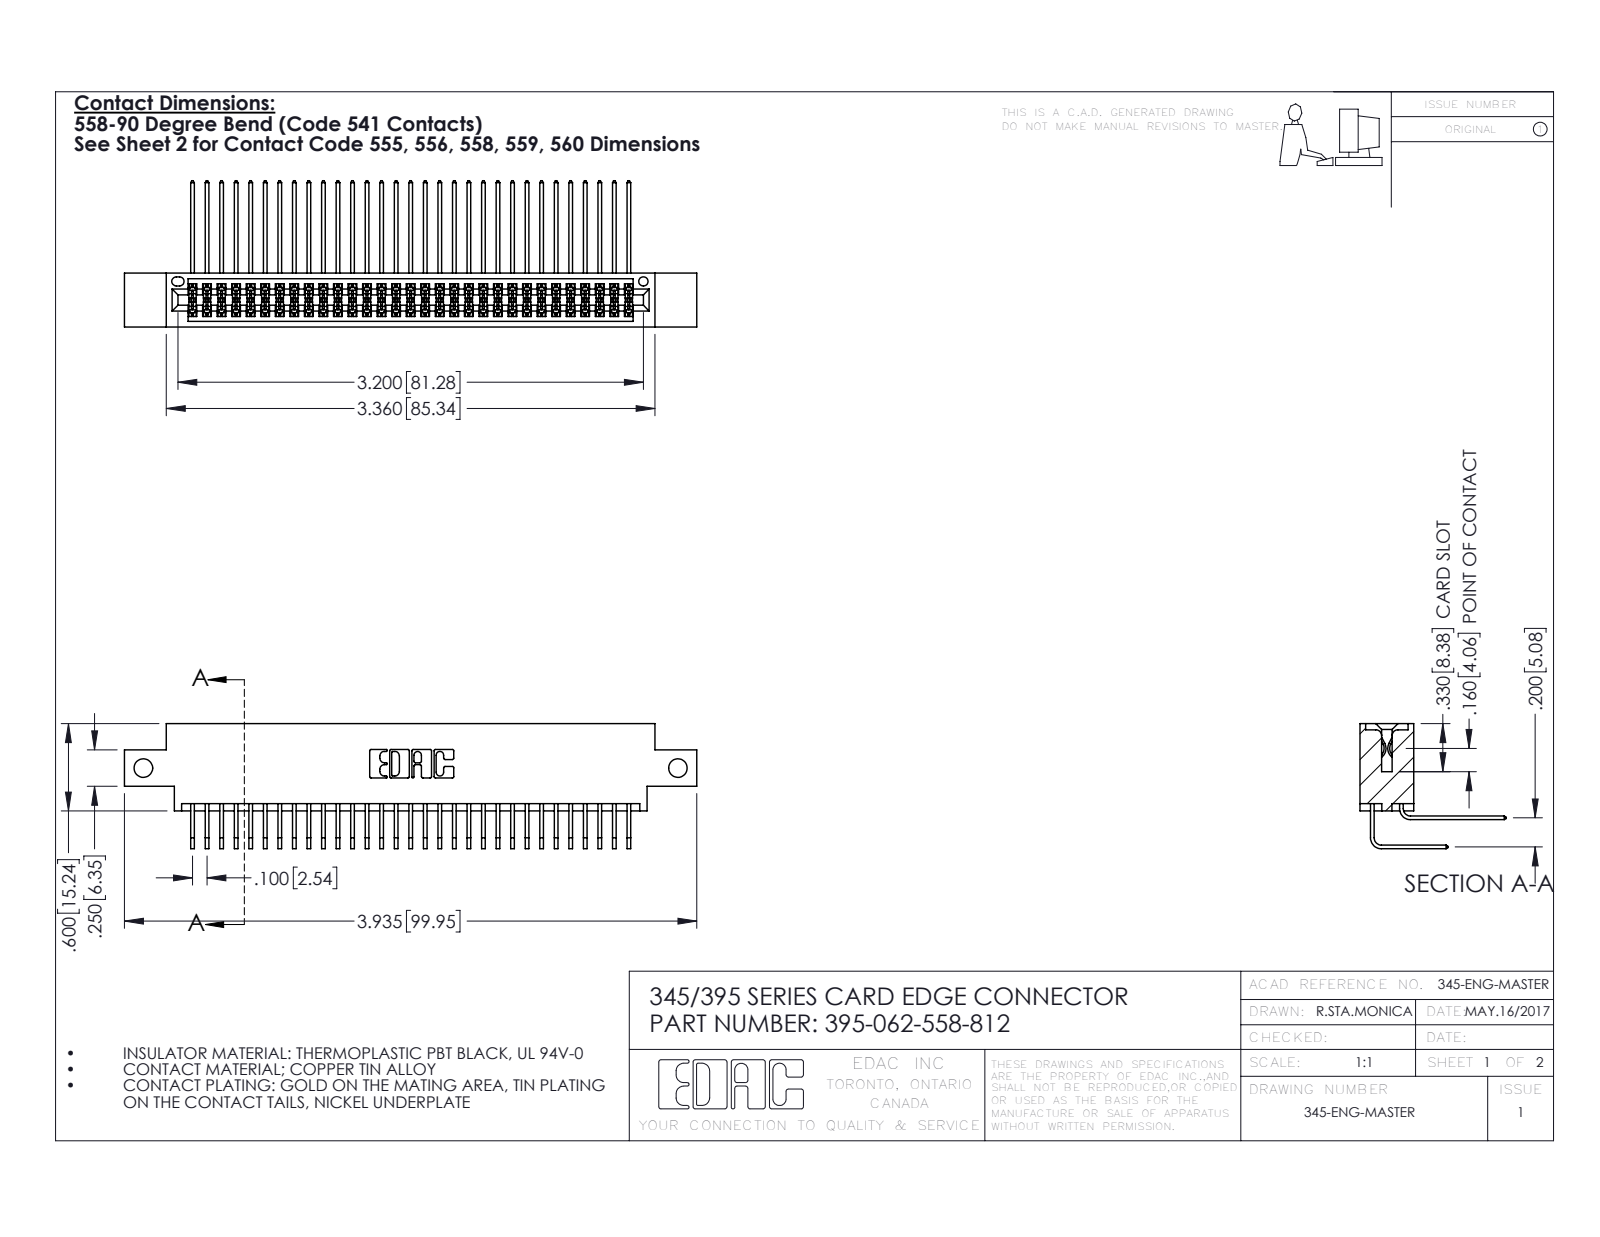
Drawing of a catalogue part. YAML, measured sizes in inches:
part_name: "345 Part_0.170 Offset - Side Mount; 345-292-001_558 Tail - 2; 395-062-558-812; 345-292-001_558 559 Tail - 1"
step_written_by: "SolidWorks 2016 (CONFIG_CONTROL_DESIGN)"
units: inches
bodies: {solids: 63, faces: 3354, planar: 2254, cylindrical: 1100, other: 0}
overall_size: [3.935, 1.005, 0.859]
volume: 0.596
surface_area: 24.66
round_holes:
  - {diameter: 0.128, count: 2}
  - {diameter: 0.064, count: 1}
partial_cylinders:
  - {radius: 0.006, count: 94}
  - {radius: 0.01, count: 22}
  - {radius: 0.007, count: 6}
  - {radius: 0.031, count: 6}
  - {radius: 0.026, count: 3}
  - {radius: 0.014, count: 2}
  - {radius: 0.019, count: 2}
  - {radius: 0.022, count: 2}
face_to_face_distances: [0.072, 0.298, 0.2, 0.37, 0.098, 0.272, 0.025, 0.225, 0.175, 0.025]
hole_center_spacings: [3.675]
